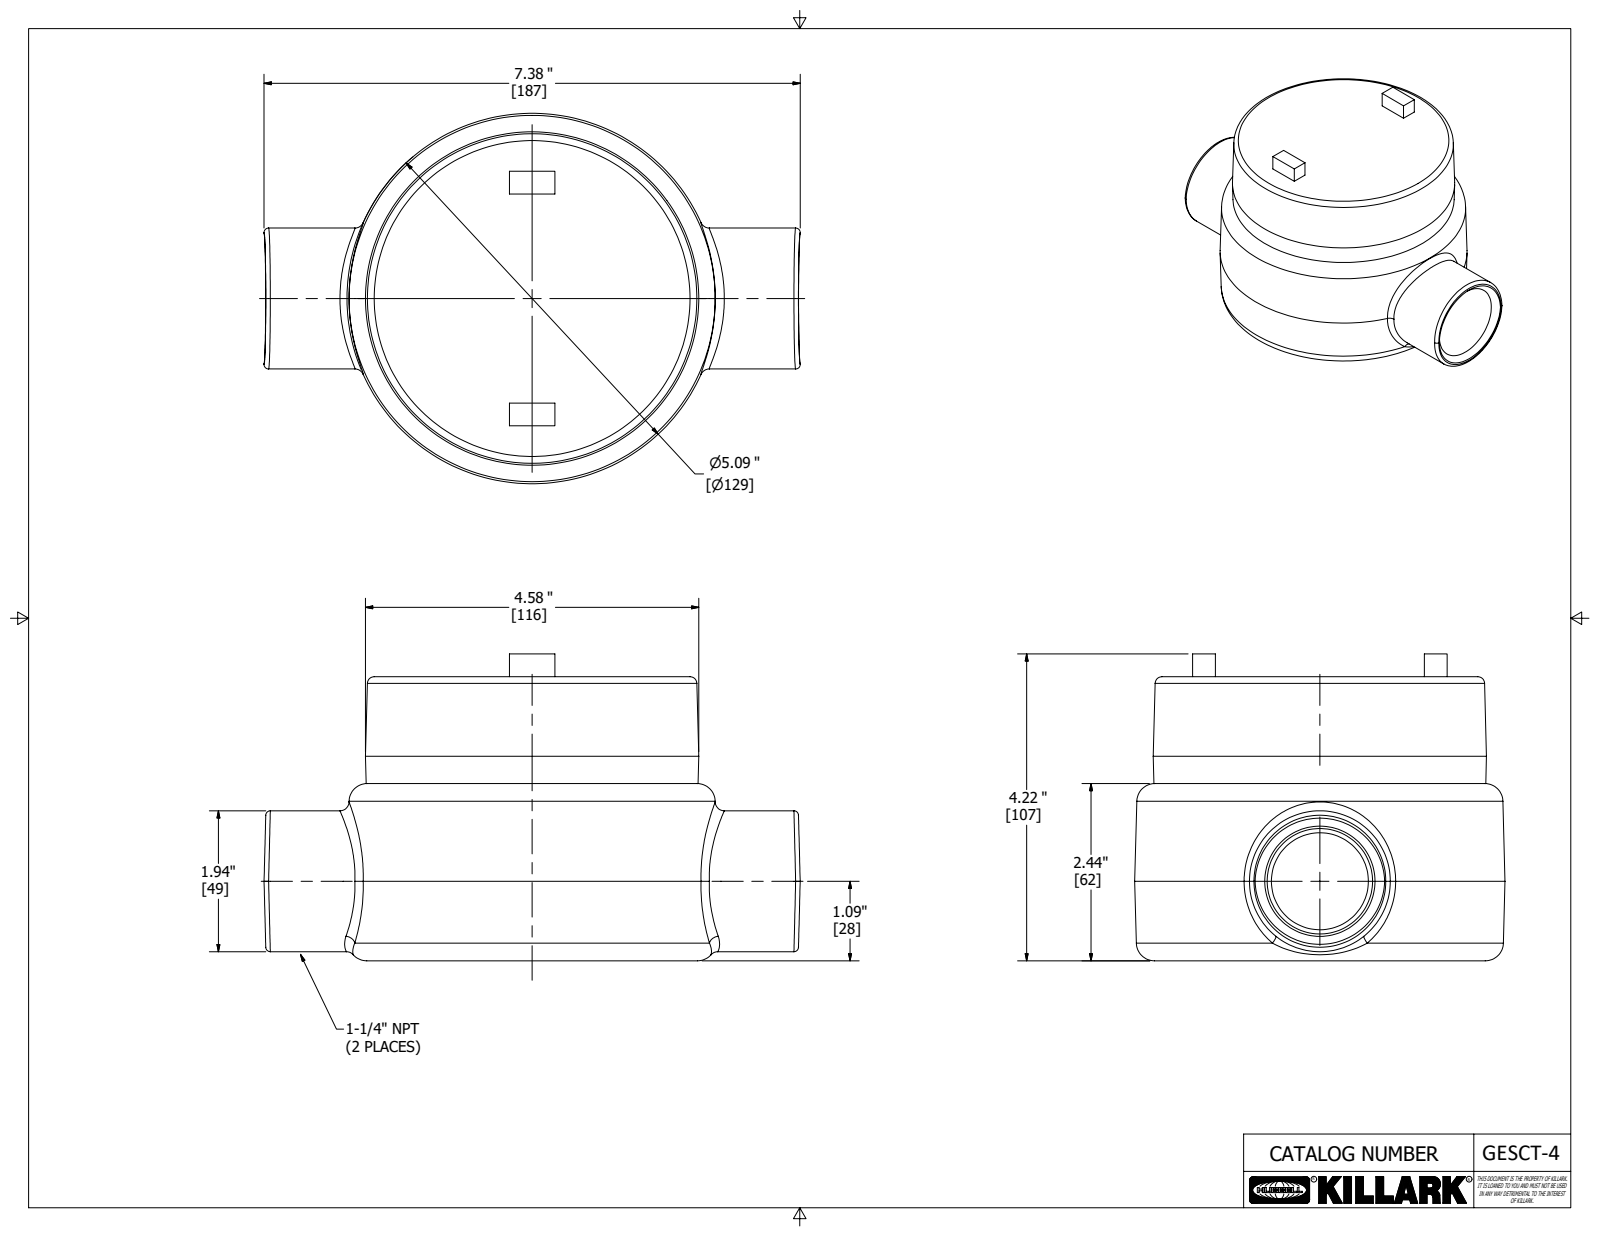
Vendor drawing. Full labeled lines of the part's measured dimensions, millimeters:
Part name (STEP PRODUCT): GESCT-4; 03979-2; 04056-11
STEP written by: Autodesk Inventor 2020 (AUTOMOTIVE_DESIGN)
Units: millimetres
Bodies: 2 solids, 667 faces (383 planar, 26 cylindrical, 258 other)
Overall size (bounding box): 187.3 × 129.4 × 107.2
Volume: 551 100 mm³ · Surface area: 145 600 mm²
Round holes (diameter × count): ⌀4.7 ×1, ⌀33.9 ×1, ⌀44.5 ×1, ⌀98 ×1, ⌀103 ×1
Round bosses / shafts (diameter × count): ⌀95.3 ×1, ⌀49.2 ×1
Partial cylindrical surfaces — rounded edges, fillets, slot ends (radius × count): R1.6 ×12, R6.4 ×1, R29.4 ×1, R38.9 ×1
Main face-to-face distances: 99.2, 90, 9.2, 88.9, 10.3, 79.7, 9.5, 0.8, 80.5, 89.7
Hole centre spacings: 35.7
